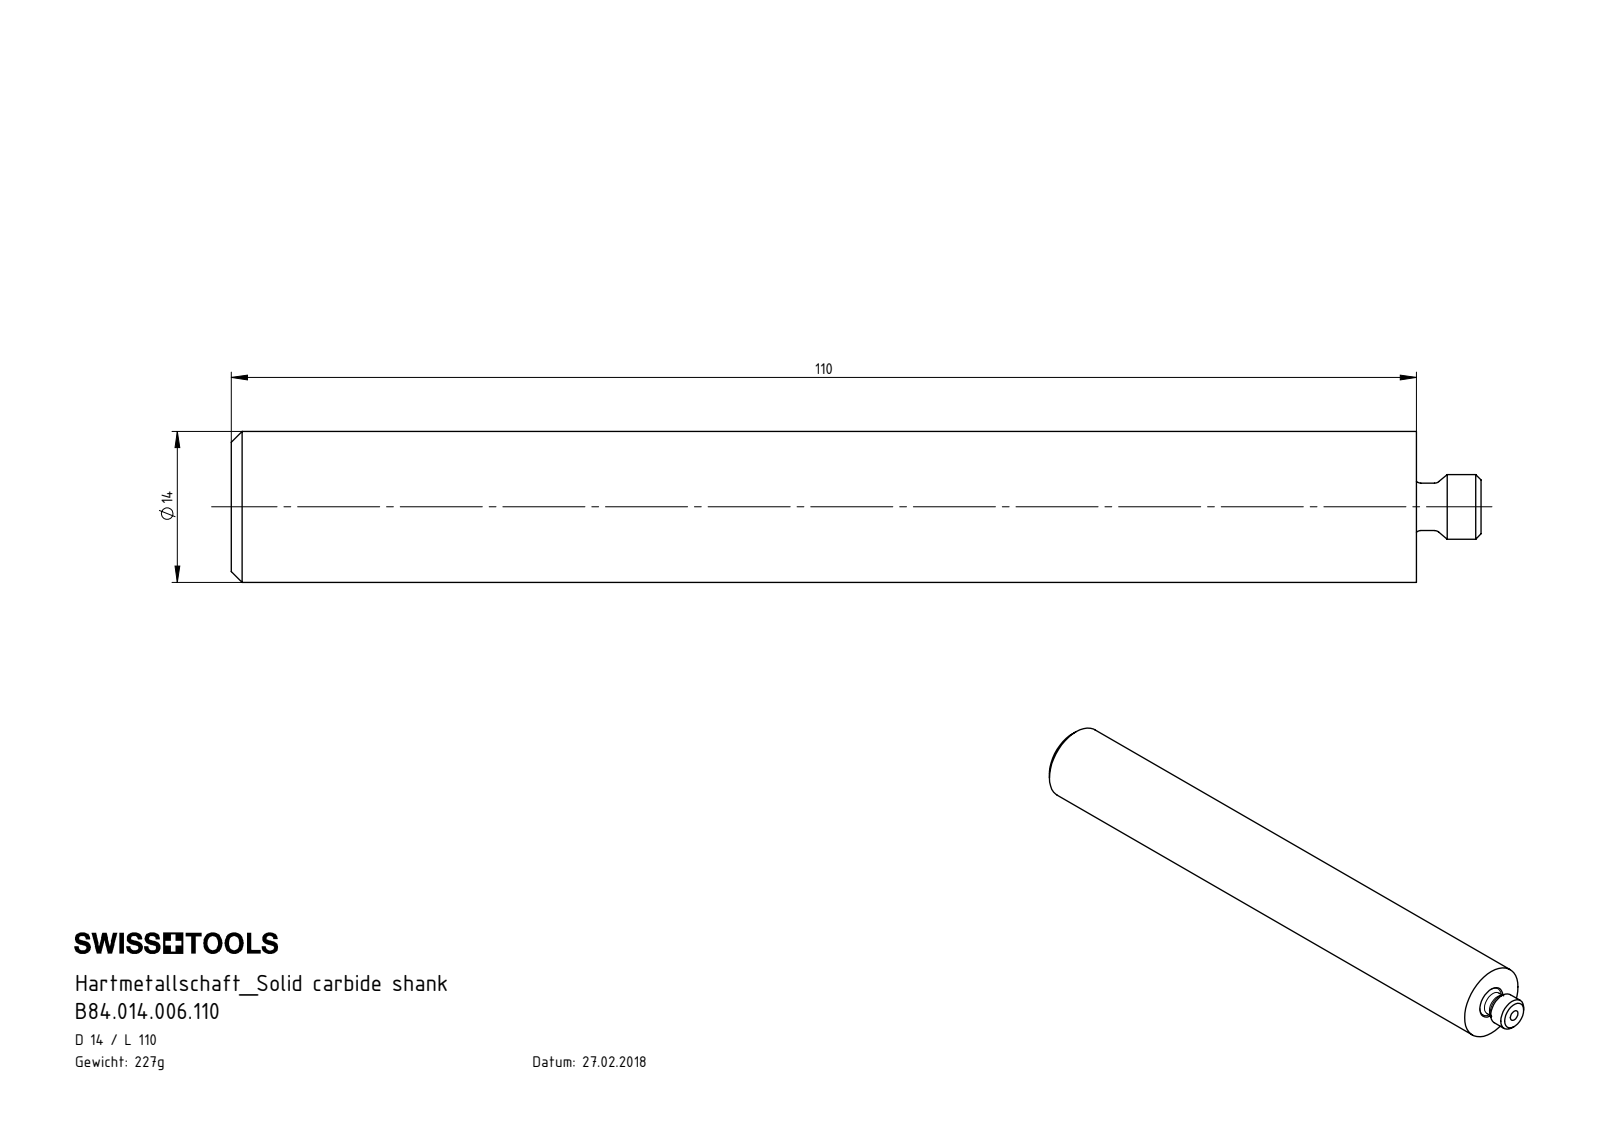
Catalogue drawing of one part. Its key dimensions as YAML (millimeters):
part_name: "HM1-U14.001.110_A; HM1-BG1.006.015_A; B84.014.006.110"
step_written_by: "SolidWorks 2017 (CONFIG_CONTROL_DESIGN)"
units: millimeters
bodies: {solids: 2, faces: 35, planar: 5, cylindrical: 14, other: 16}
overall_size: [116, 14, 14]
volume: 15787
surface_area: 6929
round_holes:
  - {diameter: 2, count: 1}
  - {diameter: 4, count: 1}
  - {diameter: 5, count: 1}
round_bosses_or_shafts:
  - {diameter: 14, count: 1}
  - {diameter: 6, count: 1}
  - {diameter: 4.4, count: 1}
face_to_face_distances: [110, 100.8, 116, 9.2, 15.2, 6, 109.8, 9, 6.2]
